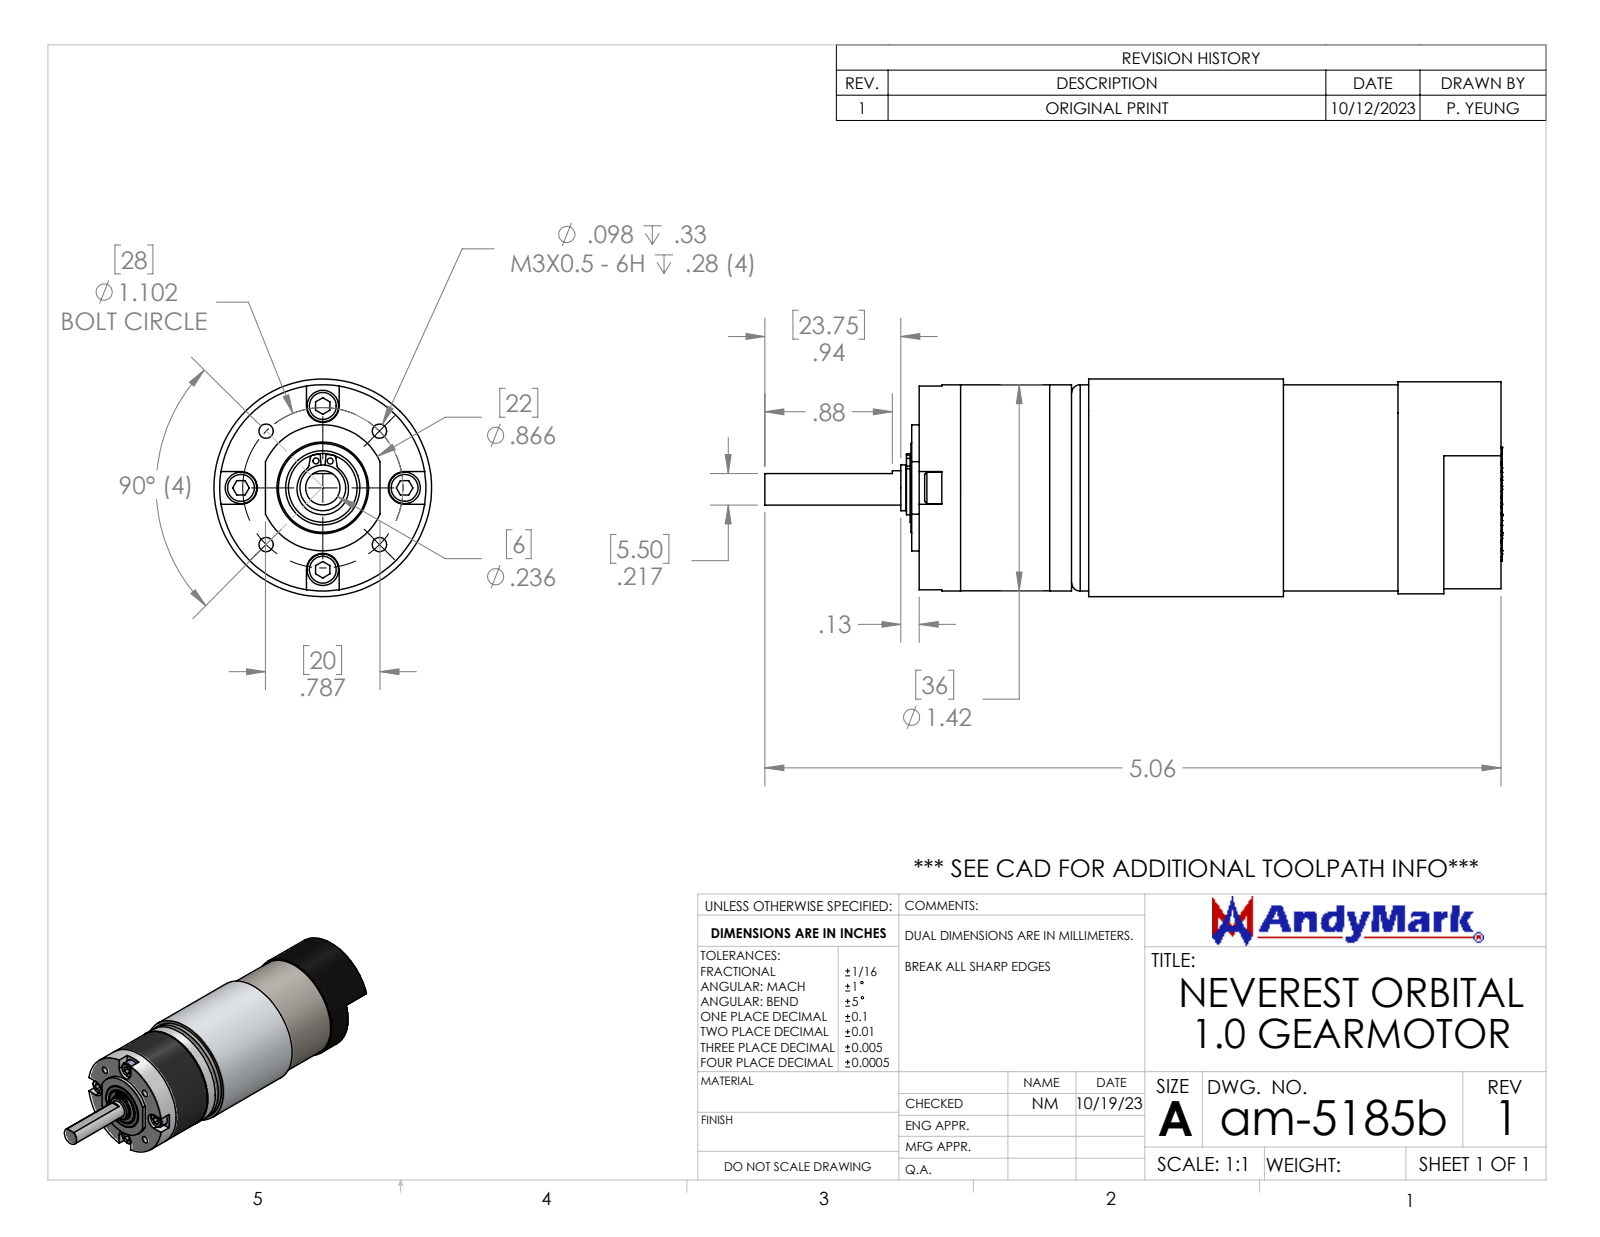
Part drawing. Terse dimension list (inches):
name: am-5182 NeveRest Orbital 1-1 Coupler; Shim; 97633A150_BLACK-FINISH STEEL EXTERNAL RETAINING RING_97633A150_grv; SHCS M3 x 16mm (+6 more)
written by: SolidWorks 2022 (AUTOMOTIVE_DESIGN)
unit: in
bodies: 26 solids, 767 faces (272 planar, 285 cylindrical, 210 other)
size: 5.069 × 1.496 × 1.496
volume: 6.49 in³; area: 36.3 in²
holes: 10× ⌀0.098, 8× ⌀0.125, 5× ⌀0.125, 2× ⌀0.041, 1× ⌀0.29, 1× ⌀0.315, 1× ⌀0.434, 1× ⌀0.511, 1× ⌀0.512, 1× ⌀0.63
bosses: 4× ⌀0.217, 4× ⌀0.118, 1× ⌀1.496, 1× ⌀1.457, 1× ⌀1.417, 1× ⌀1.415, 1× ⌀0.807, 1× ⌀0.472
rounds: 34× R0.064, 34× R0.069, 4× R0.028, 3× R0.112, 1× R0.113, 1× R0.137, 1× R0.142, 1× R0.177
face distances: 2.952, 4, 1.047, 0.394, 3.169, 0.217, 0.831, 0.197, 2.559, 2.775
hole spacings: 0.426, 1.029, 0.285, 0.409, 0.551, 0.739, 0.78, 0.269
